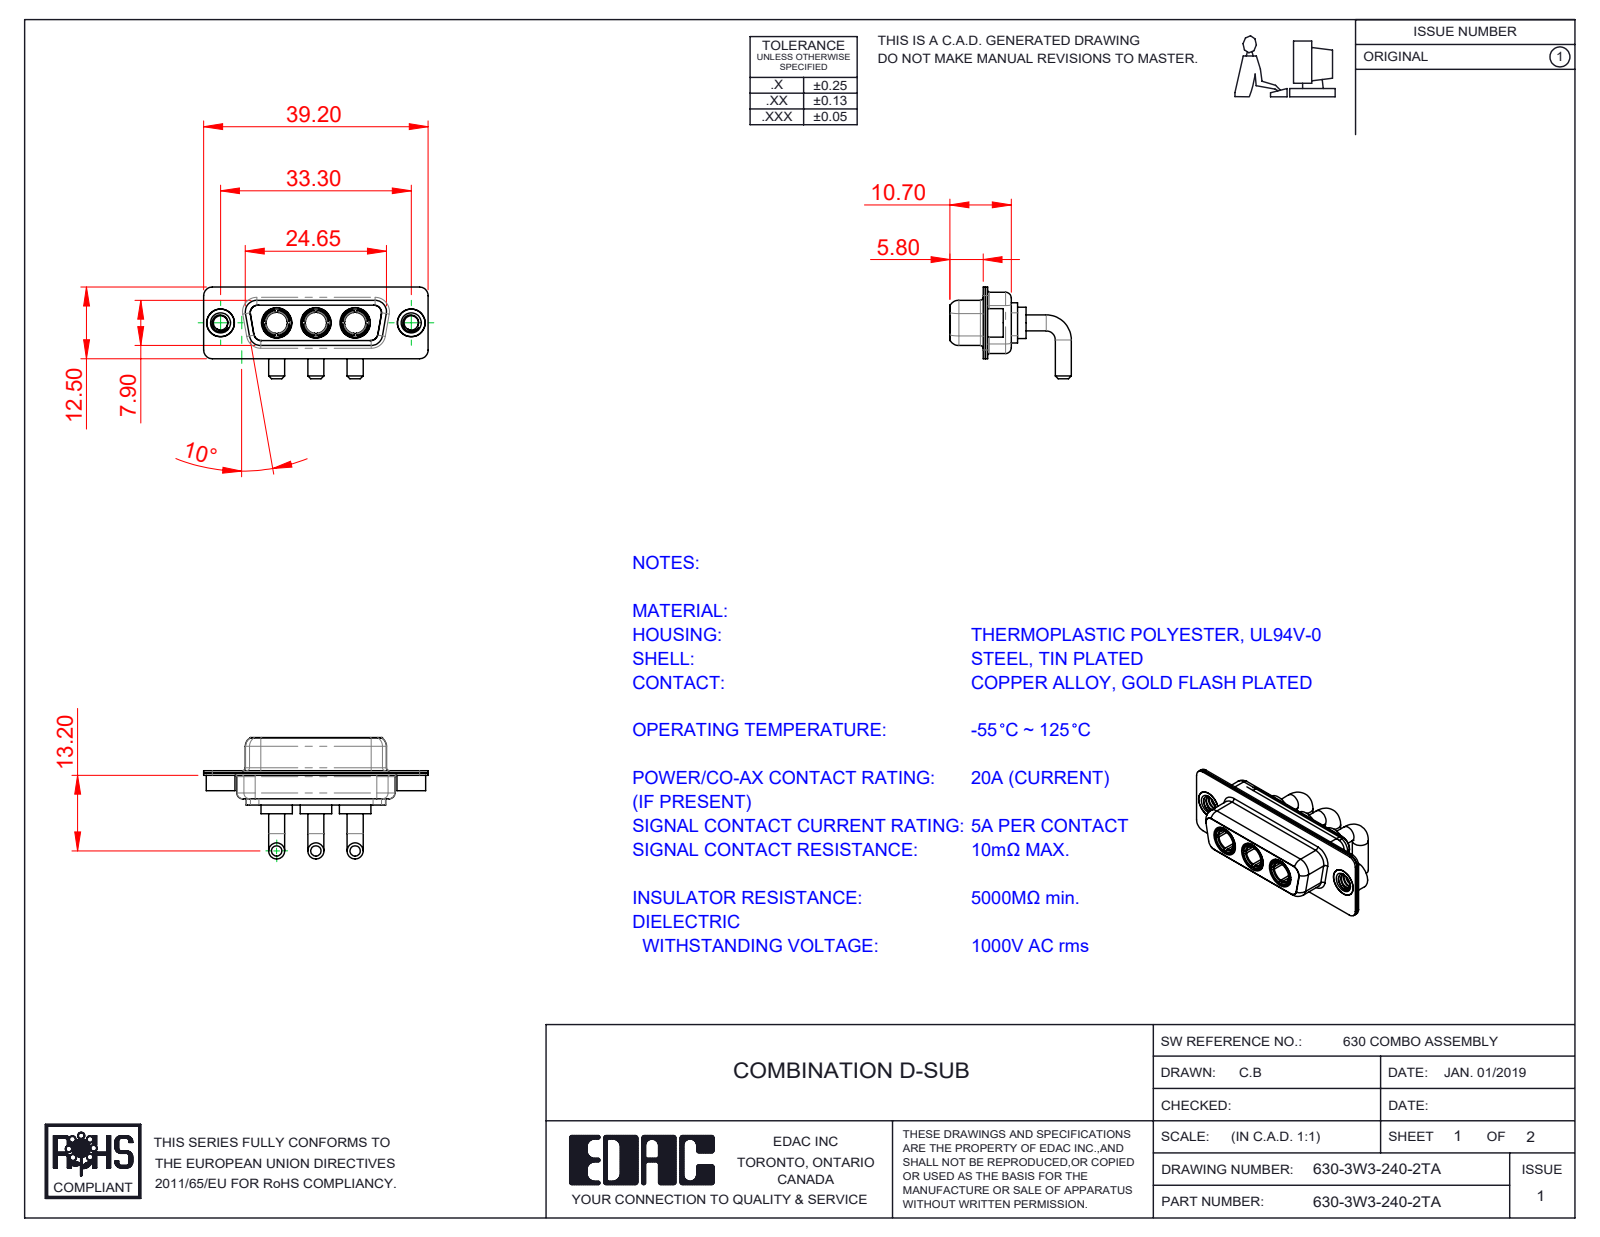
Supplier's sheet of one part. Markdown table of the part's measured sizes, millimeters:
| quantity | value |
| --- | --- |
| part name | Power Socket_20A RA; 630Combo Shell Front_15 Contacts; 630-3W3-240-2TA; 630Combo Threaded Rivet_A (+2 more) |
| STEP written by | SolidWorks 2020 (CONFIG_CONTROL_DESIGN) |
| units | millimeters |
| bodies | 11 solids, 507 faces (154 planar, 210 cylindrical, 143 other) |
| overall size | 39.2 × 21.2 × 16 |
| volume | 2 636 mm³ |
| surface area | 5 928 mm² |
| round holes (diameter × count) | 4.85 × 5, 3.7 × 3, 5.3 × 3, 2.5 × 2, 4 × 2, 4.05 × 2 |
| round bosses / shafts (diameter × count) | 2.8 × 6, 5.5 × 3, 5.2 × 3, 4.96 × 3, 4.75 × 3, 3.75 × 3, 5 × 2, 4.95 × 2 |
| partial cylindrical surfaces (radius × count) | 1.5 × 16, 1.35 × 12, 2 × 12, 1.6 × 8, 0.25 × 4, 0.5 × 4, 0.6 × 4, 0.65 × 4 |
| main face-to-face distances | 0.4, 1.4, 0.45, 8.45, 8.9, 1.8, 7.05, 0.8, 6.2, 7.5 |
| hole center spacings | 6.85, 9.8, 16.65, 23.5, 13.7, 33.3 |
